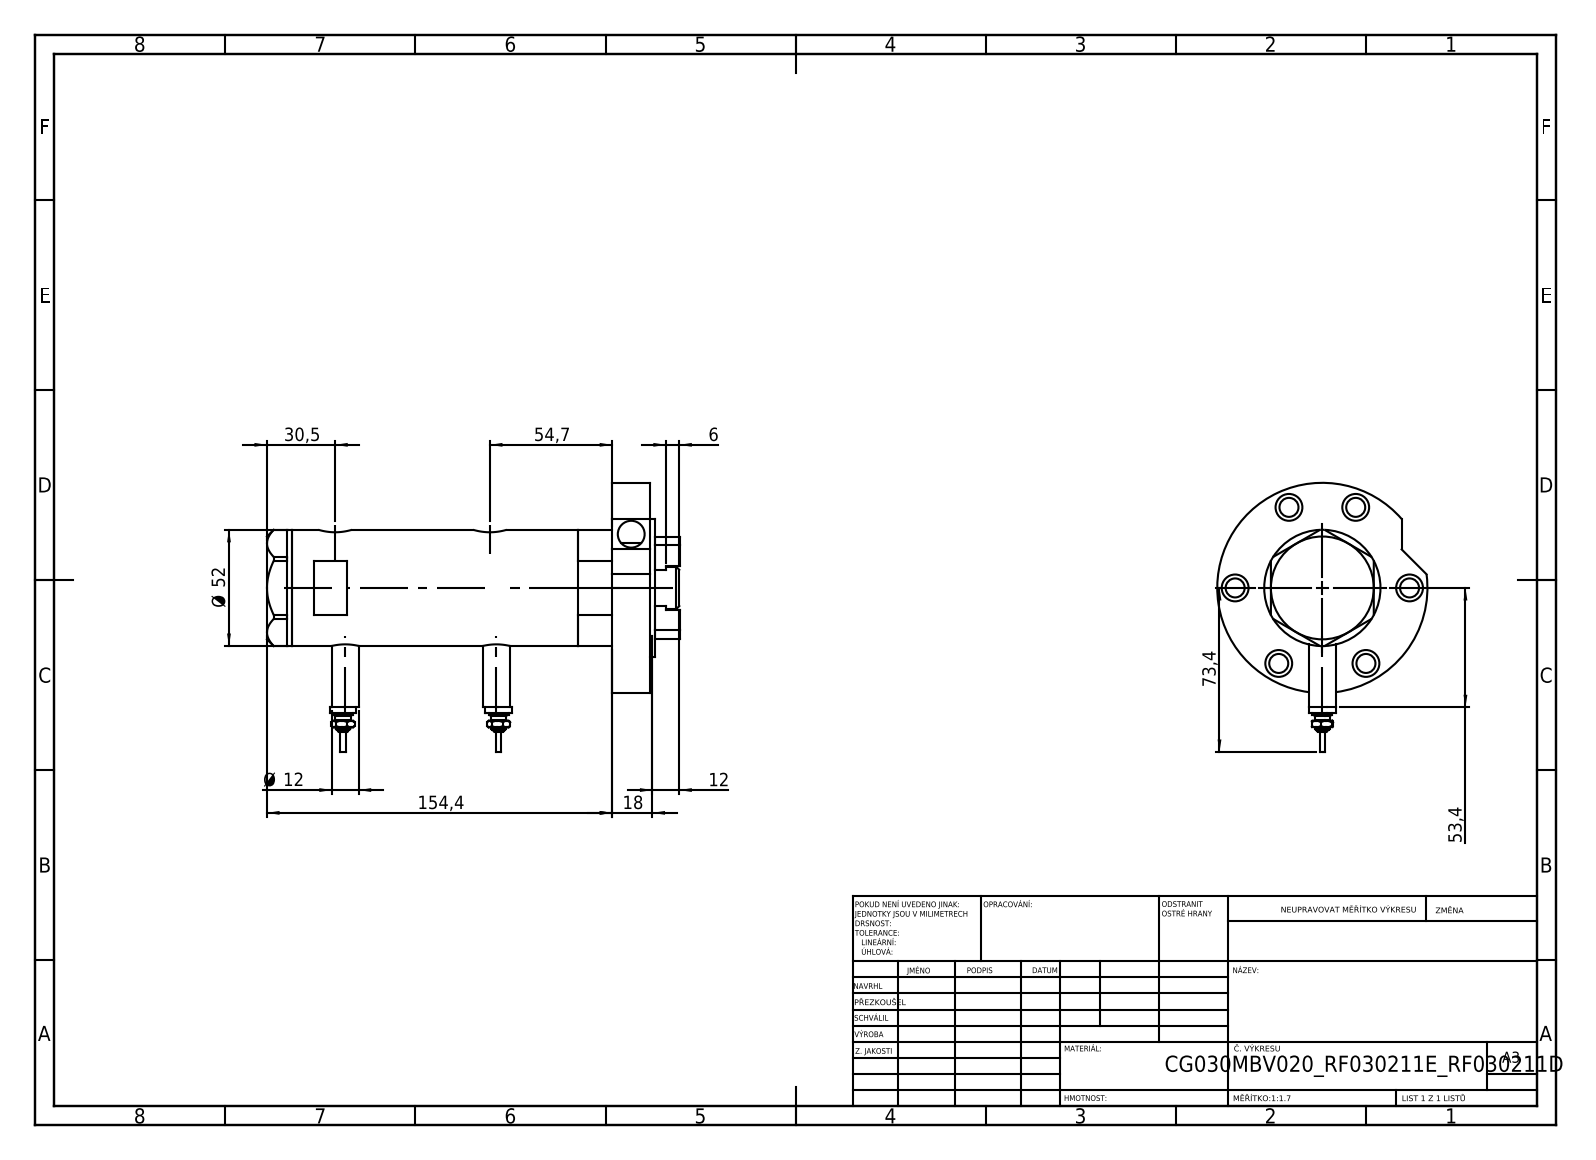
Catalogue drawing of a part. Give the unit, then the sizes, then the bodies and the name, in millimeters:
Units: millimetres
Overall size (bounding box): 184.6 × 120.4 × 94
Round holes (diameter × count): ⌀12 ×7, ⌀8.5 ×6, ⌀5.1 ×4, ⌀9 ×4, ⌀9.73 ×2, ⌀12.5 ×2, ⌀15 ×2, ⌀6.5 ×1, ⌀20 ×1, ⌀21.5 ×1, ⌀30 ×1, ⌀33 ×1
Round bosses / shafts (diameter × count): ⌀12 ×4, ⌀9 ×2, ⌀7 ×2, ⌀4.5 ×2, ⌀2.5 ×2, ⌀94 ×1, ⌀62 ×1, ⌀52 ×1
Main face-to-face distances: 17, 143.4, 160.4, 2, 11, 162.4, 91.5, 51.9, 68.9, 173.4
Hole centre spacings: 39, 16.74, 37.57, 46.81, 10, 22.37, 22.95, 28.26
Volume: 430 950 mm³ · Surface area: 107 428 mm²
Bodies: 9 solids, 310 faces (128 planar, 118 cylindrical, 64 other)
Part name (STEP PRODUCT): V270CG_MIDDLE; V270CG_RF211D; V270CG_BACK; V270CG_FRONT (+3 more)
STEP written by: SolidWorks 2019 (CONFIG_CONTROL_DESIGN)
